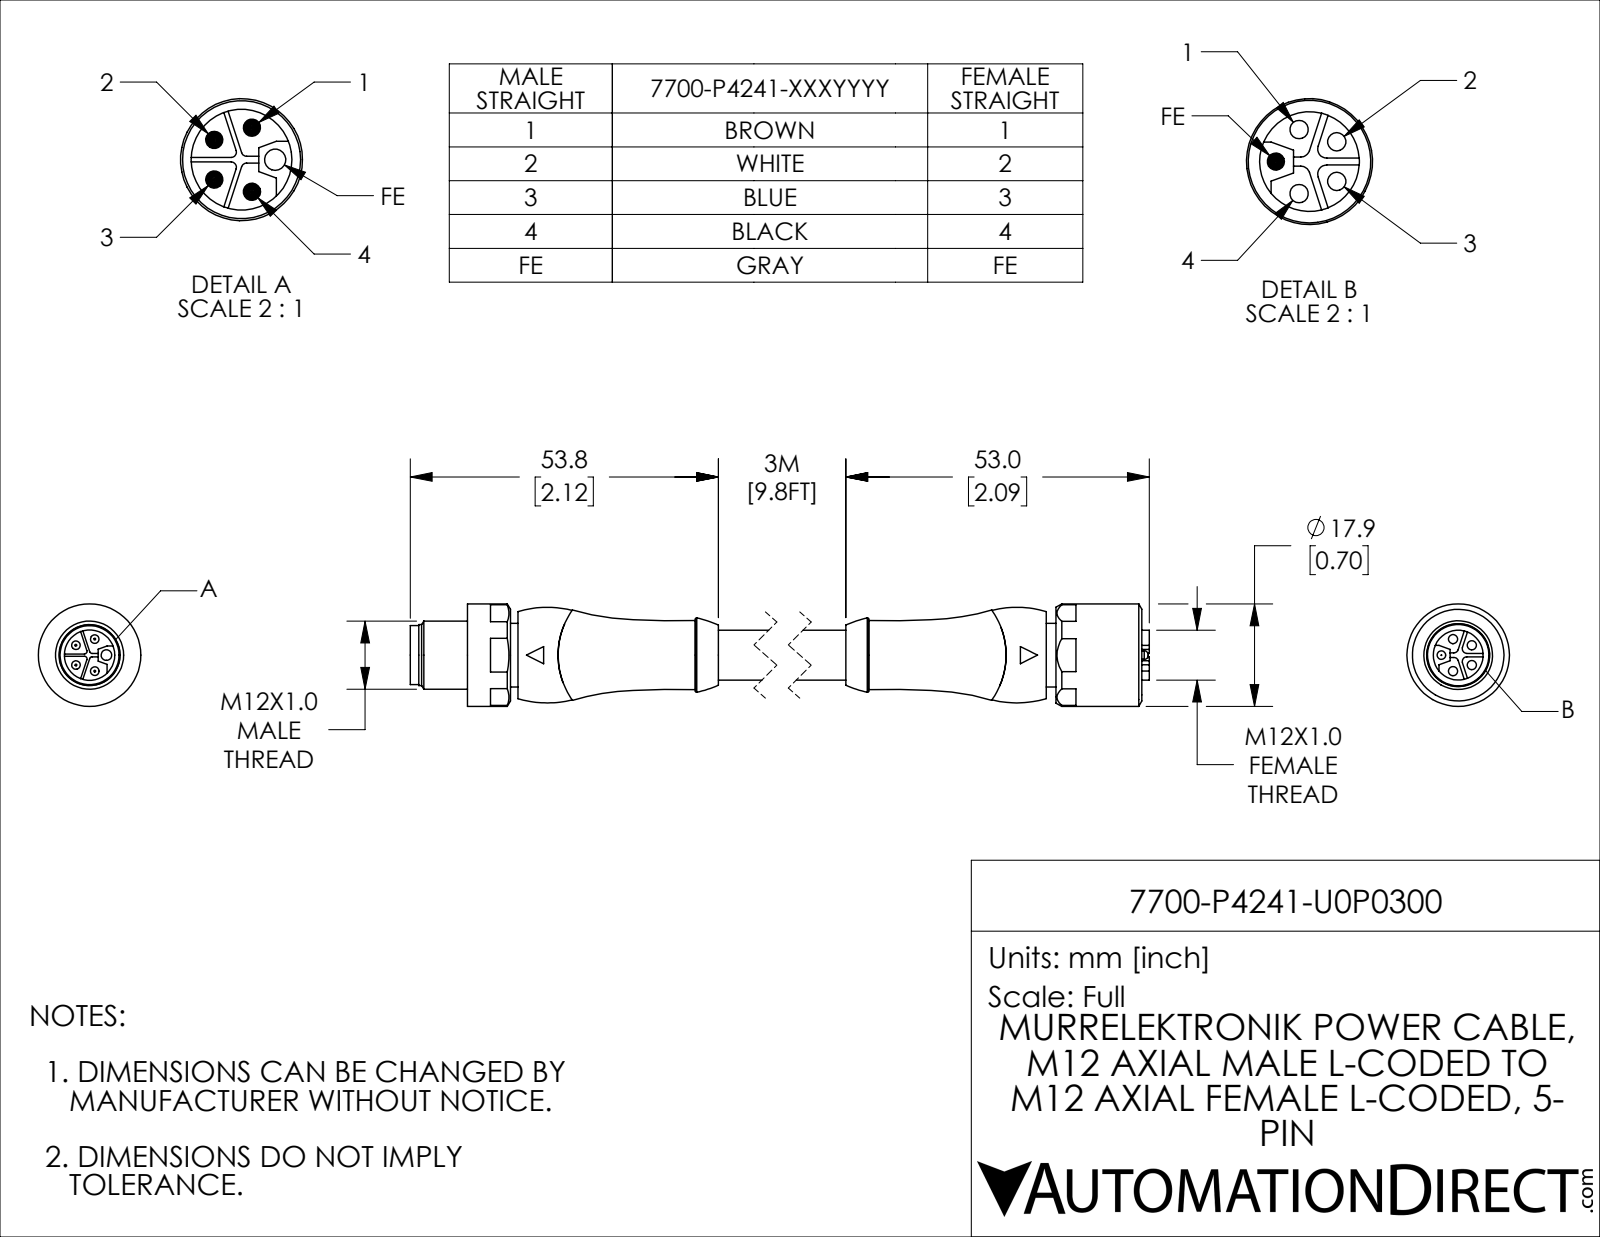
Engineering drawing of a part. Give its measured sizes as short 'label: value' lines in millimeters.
name: 7700-P4241-U0P0300_1; 7700-P4241-U0P0300; 7700-P4241-U0P0300_2
written by: SolidWorks 2021 (CONFIG_CONTROL_DESIGN)
unit: mm
bodies: 3 solids, 214 faces (98 planar, 62 cylindrical, 54 other)
size: 136.8 × 17.9 × 17.9
volume: 17 860 mm³; area: 9 316 mm²
holes: 4× ⌀1.6, 1× ⌀1.9, 1× ⌀8.8, 1× ⌀11, 1× ⌀13
bosses: 5× ⌀1.5, 1× ⌀17.9, 1× ⌀13, 1× ⌀11.9, 1× ⌀11.1, 1× ⌀10.6, 1× ⌀10.3, 1× ⌀8.7
rounds: 4× R0.5, 4× R0.8
face distances: 108.8, 1.7, 8.8, 16.9, 1.3, 7.5, 5.8, 125.5, 16.7, 110.5
hole spacings: 2.9, 3.5, 5.6, 5.6
